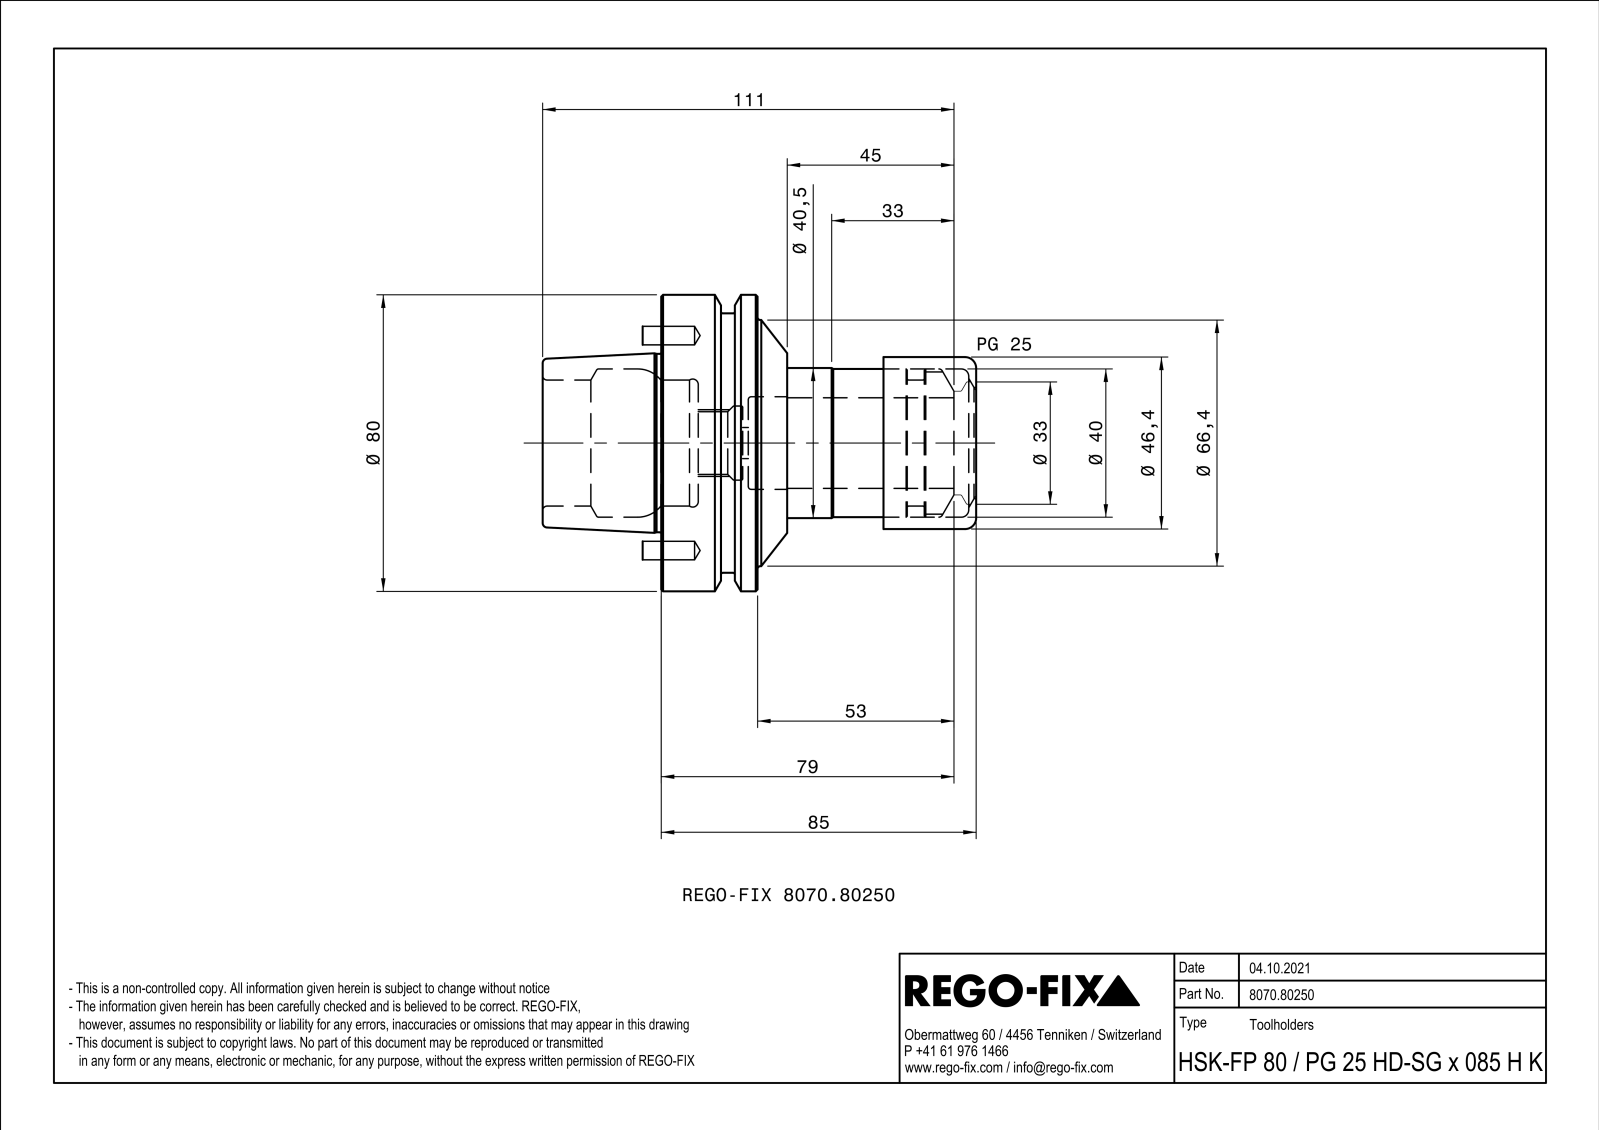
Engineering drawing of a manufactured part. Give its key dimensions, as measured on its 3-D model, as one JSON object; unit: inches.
{"part_name": "0023460", "step_written_by": "SIEMENS PLM Software Solid Edge ST10 (AUTOMOTIVE_DESIGN)", "units": "inches", "bodies": {"solids": 6, "faces": 107, "planar": 32, "cylindrical": 32, "other": 43}, "overall_size": [4.606, 3.15, 3.15], "volume_in3": 11.8, "surface_area_in2": 76.05, "round_holes": [[0.157, 2], [0.177, 2], [0.197, 2], [0.331, 1], [0.666, 1], [0.787, 1], [0.984, 1], [1.181, 1], [1.339, 1], [1.511, 1], [1.577, 1], [1.654, 1]], "round_bosses_or_shafts": [[0.177, 2], [3.15, 1], [2.756, 1], [2.614, 1], [1.895, 1], [1.827, 1], [1.811, 1], [1.594, 1]], "face_to_face_distances": [1.024, 1.339, 0.241, 0.389, 0.315, 0.472, 2.008, 0.945, 0.63, 0.394], "hole_center_spacings": [1.142, 2.283]}
